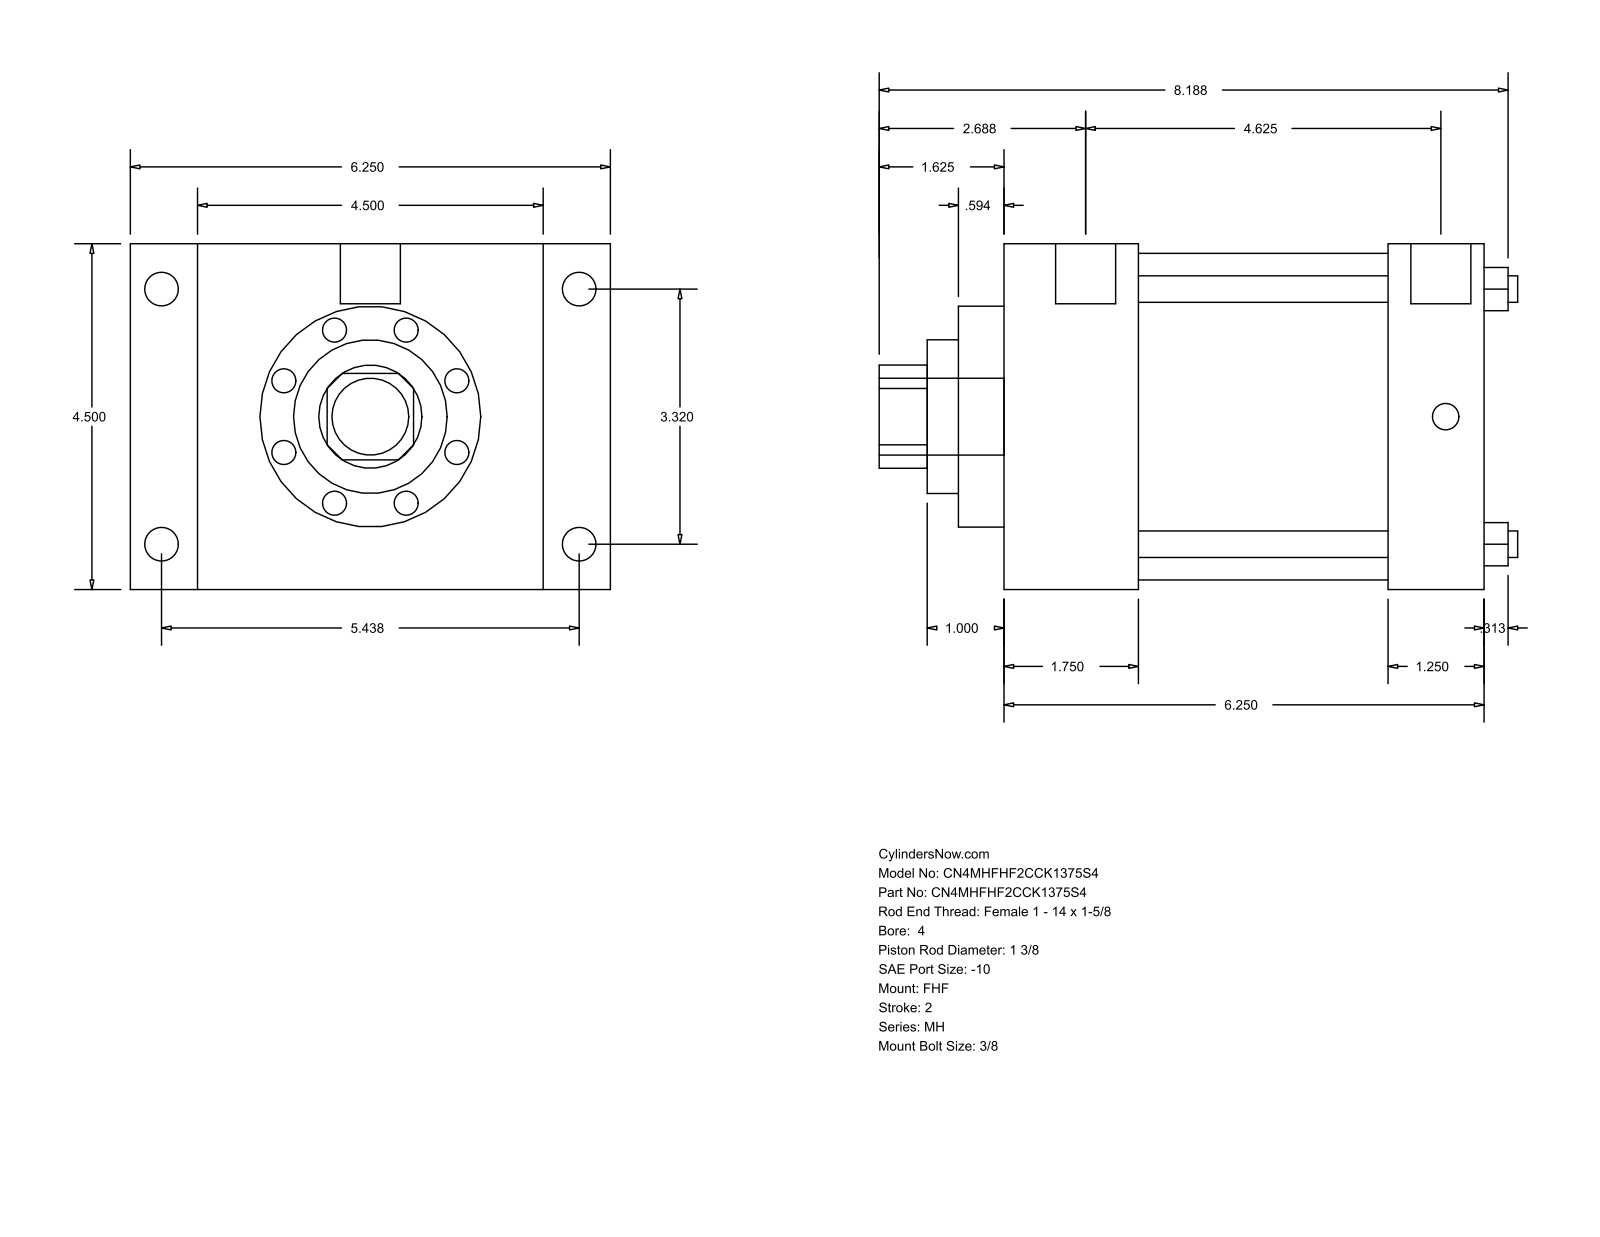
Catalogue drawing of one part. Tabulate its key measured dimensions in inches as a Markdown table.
| quantity | value |
| --- | --- |
| part name | MH_FHF__0400_1.375 |
| STEP written by | GSSL Pune (CONFIG_CONTROL_DESIGN) |
| units | inches |
| bodies | 0 solids, 90 faces (61 planar, 29 cylindrical, 0 other) |
| overall size | 8.313 × 6.25 × 4.5 |
| round holes (diameter × count) | 0.345 × 4, 1.375 × 1, 2 × 1, 2.875 × 1, 4.25 × 1 |
| round bosses / shafts (diameter × count) | 0.438 × 4, 0.344 × 4, 0.781 × 2, 1 × 1 |
| partial cylindrical surfaces (radius × count) | 0.672 × 1 |
| main face-to-face distances | 6.25, 4.5, 1.75, 4.5, 0.875, 5.375, 5, 3.25, 1.25, 0.594 |
| hole center spacings | 2.347, 3.32, 4.695 |
